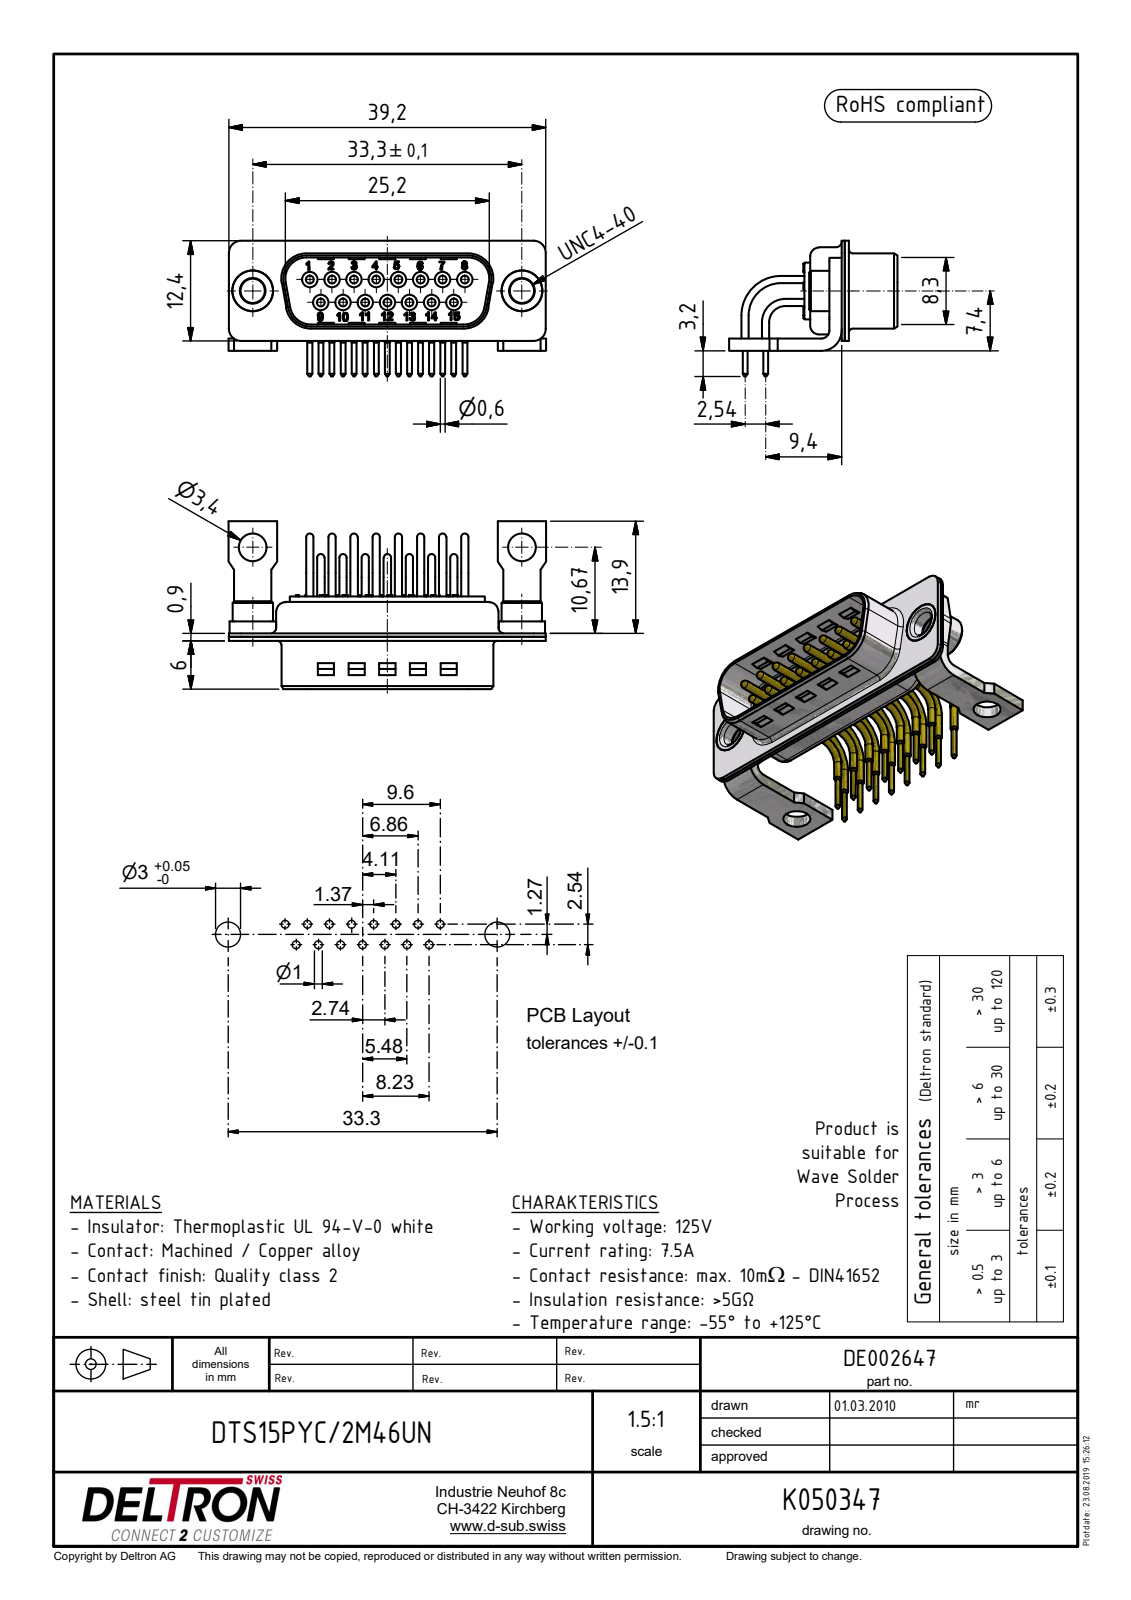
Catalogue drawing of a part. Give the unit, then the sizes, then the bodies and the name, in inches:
Units: inches
Overall size (bounding box): 1.547 × 0.819 × 0.661
Round holes (diameter × count): ⌀0.076 ×15, ⌀0.091 ×15, ⌀0.013 ×2, ⌀0.118 ×2, ⌀0.126 ×2, ⌀0.134 ×2, ⌀0.159 ×2, ⌀0.16 ×2, ⌀0.009 ×1, ⌀0.011 ×1
Round bosses / shafts (diameter × count): ⌀0.035 ×30, ⌀0.077 ×15, ⌀0.076 ×15, ⌀0.063 ×15, ⌀0.063 ×15, ⌀0.039 ×15, ⌀0.024 ×15, ⌀0.197 ×2
Partial cylindrical surfaces — rounded edges, fillets, slot ends (radius × count): R0.079 ×20, R0.042 ×15, R0.039 ×9, R0.01 ×8, R0.02 ×8, R0.028 ×8, R0.043 ×8, R0.047 ×4
Main face-to-face distances: 0.02, 0.016, 0.035, 0.059, 0.026, 0.396, 0.049, 0.094, 0.346, 0.024
Hole centre spacings: 0.124, 0.108, 0.197, 0.216, 0.292, 0.324, 0.394, 0.431
Volume: 0.127 in³ · Surface area: 9.151 in²
Bodies: 22 solids, 2805 faces (1666 planar, 834 cylindrical, 305 other)
Part name (STEP PRODUCT): N00403_BG; R+B00913_BG; R+B00914_BG; R+B00153_BG (+4 more)
STEP written by: Autodesk Inventor 2015 (AUTOMOTIVE_DESIGN)
